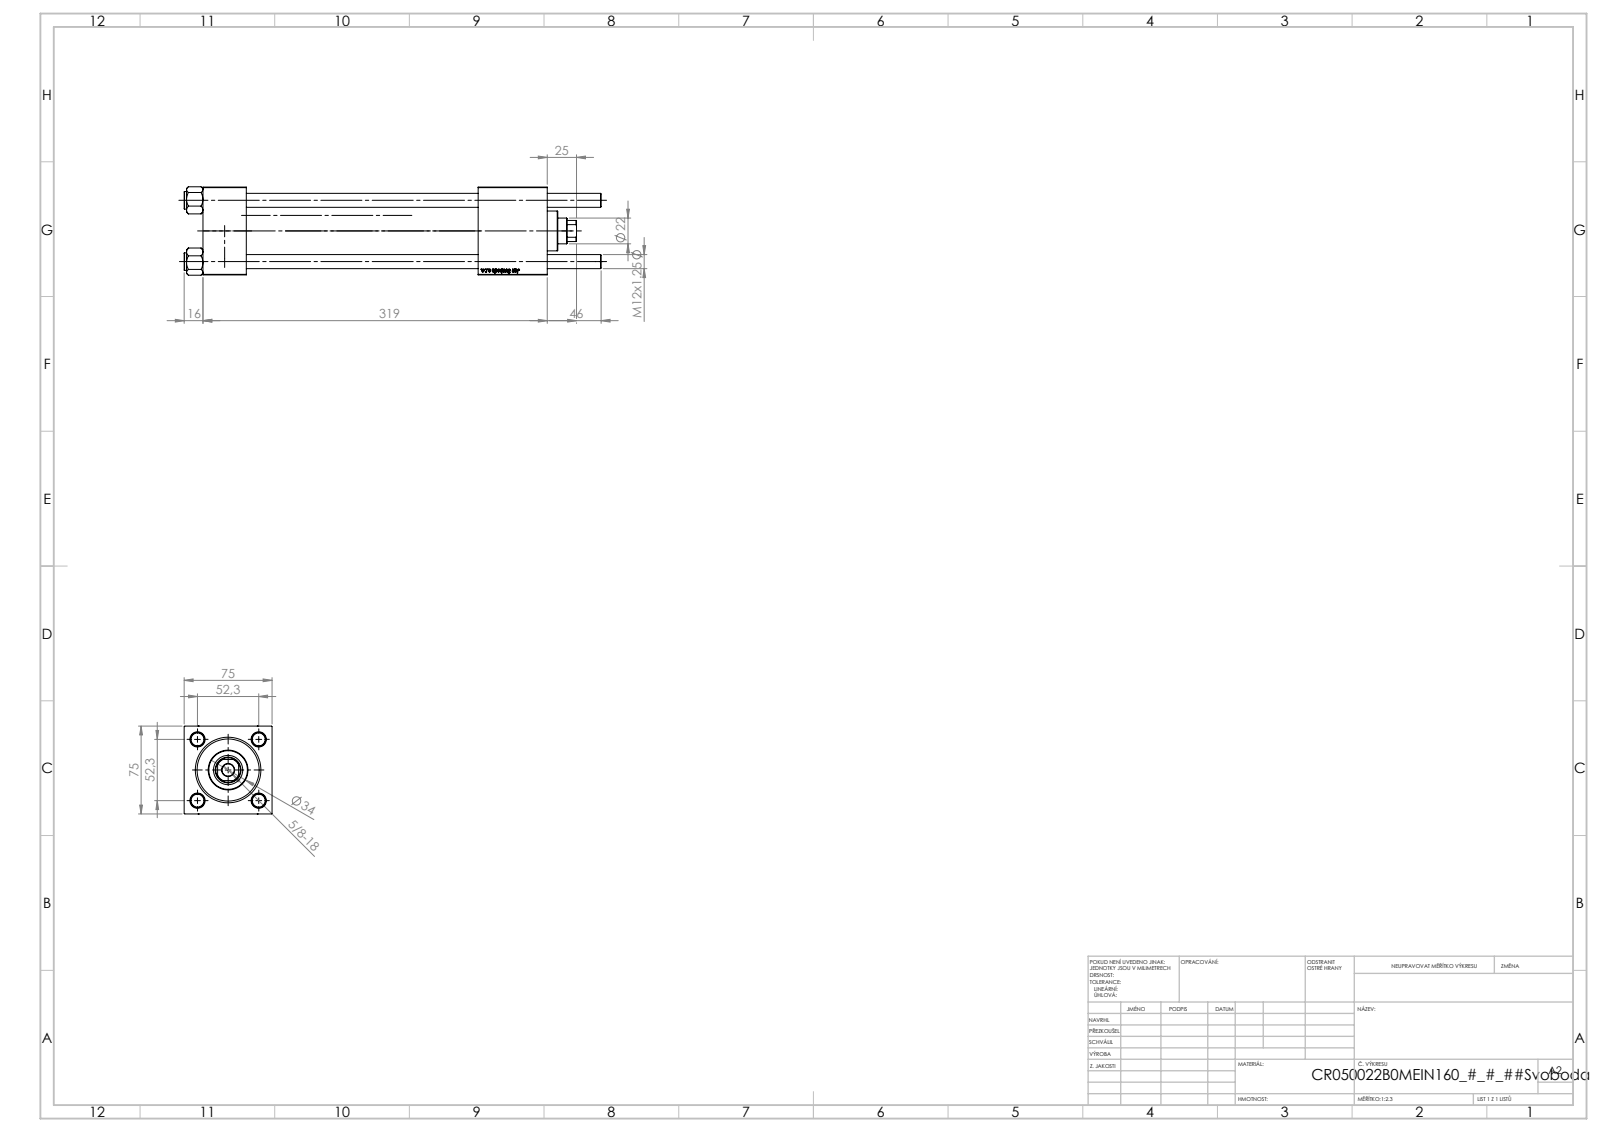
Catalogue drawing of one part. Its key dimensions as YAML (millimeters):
part_name: "NUT_M5_B; V215CR_B_TYCINKA; V215_VC_A; V215CR_VCP_B (+1 more)"
step_written_by: "SolidWorks 2019 (CONFIG_CONTROL_DESIGN)"
units: millimeters
bodies: {solids: 11, faces: 1157, planar: 430, cylindrical: 79, other: 648}
overall_size: [356, 75.45, 75]
volume: 875536
surface_area: 240578
round_holes:
  - {diameter: 12, count: 4}
  - {diameter: 7, count: 2}
  - {diameter: 20.96, count: 2}
  - {diameter: 30, count: 2}
  - {diameter: 10.5, count: 1}
  - {diameter: 22, count: 1}
  - {diameter: 25, count: 1}
  - {diameter: 41, count: 1}
  - {diameter: 50, count: 1}
  - {diameter: 53, count: 1}
round_bosses_or_shafts:
  - {diameter: 15, count: 4}
  - {diameter: 56, count: 1}
  - {diameter: 34, count: 1}
partial_cylinders:
  - {radius: 10.5, count: 1}
face_to_face_distances: [75, 37, 294, 257, 235, 198, 59, 265.3, 228.3, 30.3]
hole_center_spacings: [36.98, 52.3, 73.96, 233.5]
